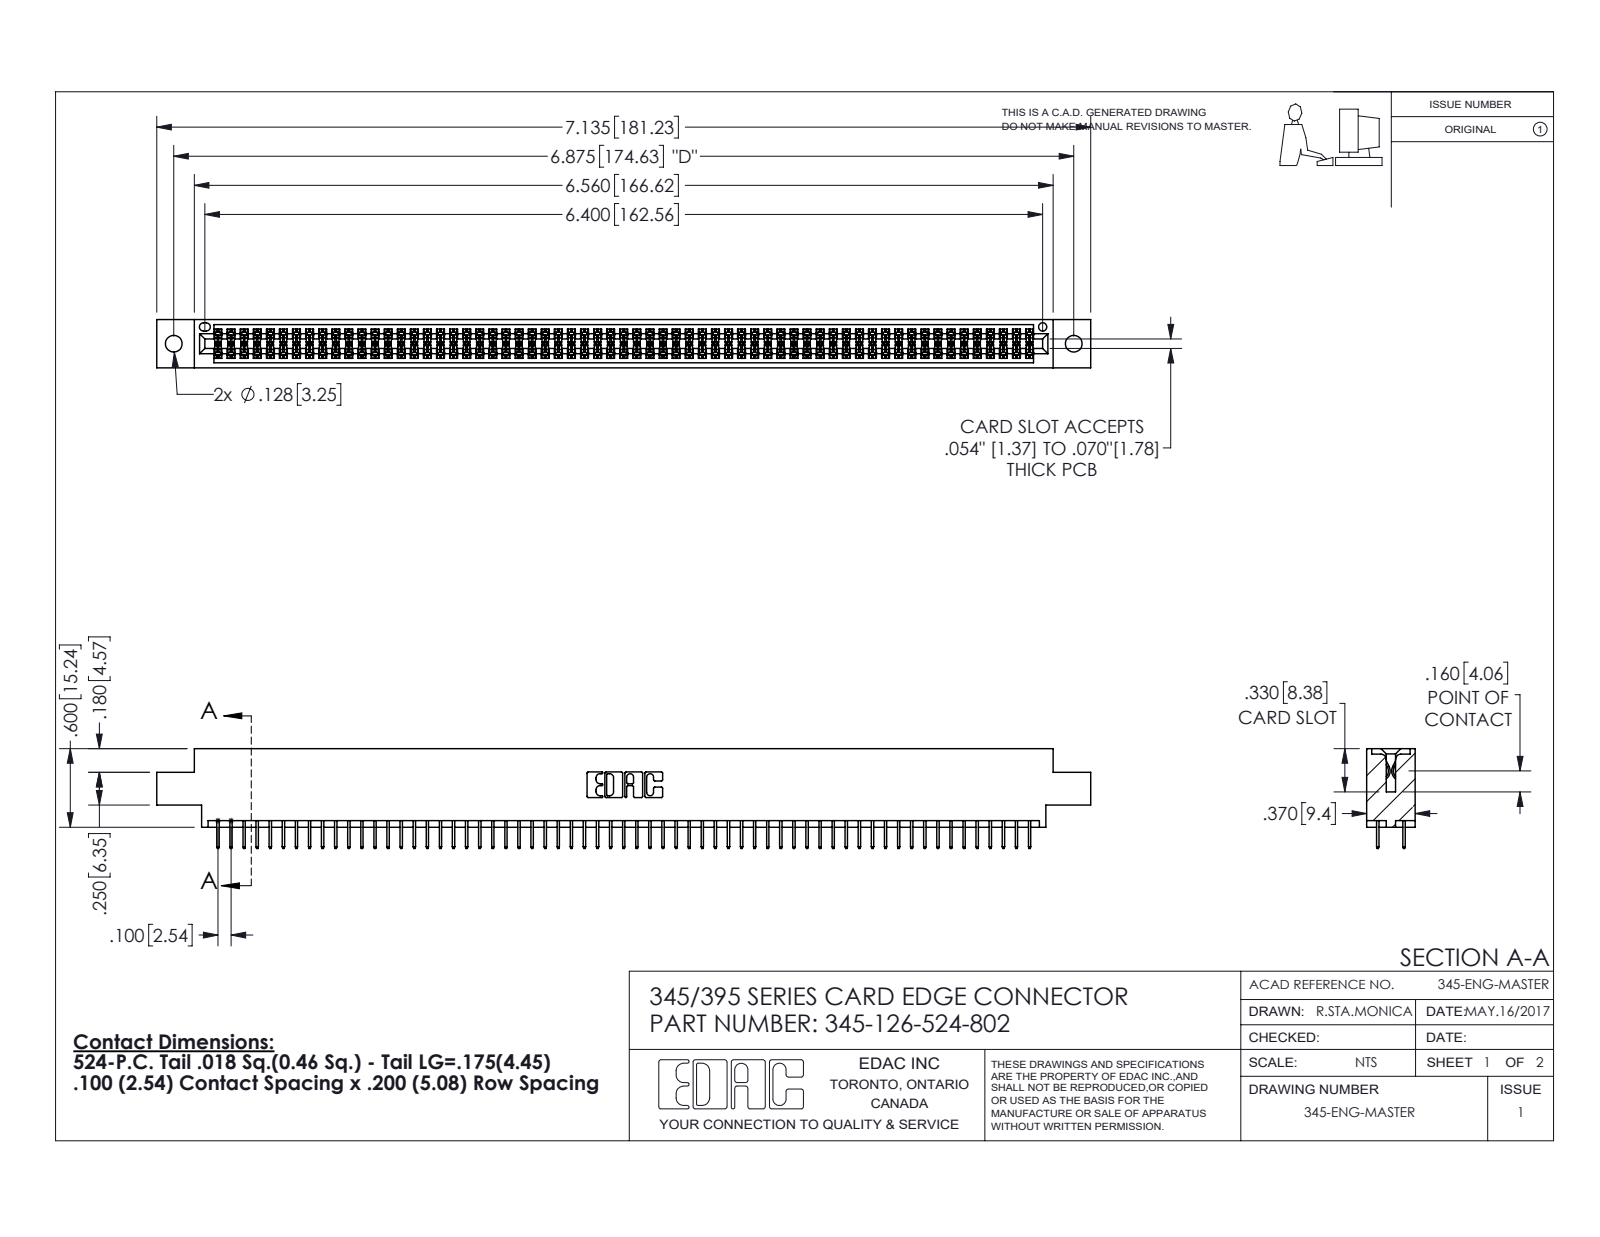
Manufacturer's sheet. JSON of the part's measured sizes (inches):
{"part_name": "345-292-001_345-293-124; 345-126-524-802; 345 Part_0.170 Offset - 0.128 Dia", "step_written_by": "SolidWorks 2016 (CONFIG_CONTROL_DESIGN)", "units": "inches", "bodies": {"solids": 127, "faces": 6934, "planar": 4998, "cylindrical": 1936, "other": 0}, "overall_size": [7.135, 0.762, 0.37], "volume_in3": 1.065, "surface_area_in2": 39.65, "round_holes": [[0.128, 2], [0.064, 1]], "partial_cylinders_radius": [[0.006, 189], [0.01, 22], [0.007, 6], [0.031, 6], [0.026, 3], [0.014, 2], [0.019, 2], [0.022, 2]], "face_to_face_distances": [0.072, 0.298, 0.37, 0.2, 0.098, 0.272, 0.025, 0.225, 0.072, 0.175], "hole_center_spacings": [0.27, 6.639, 6.875]}
